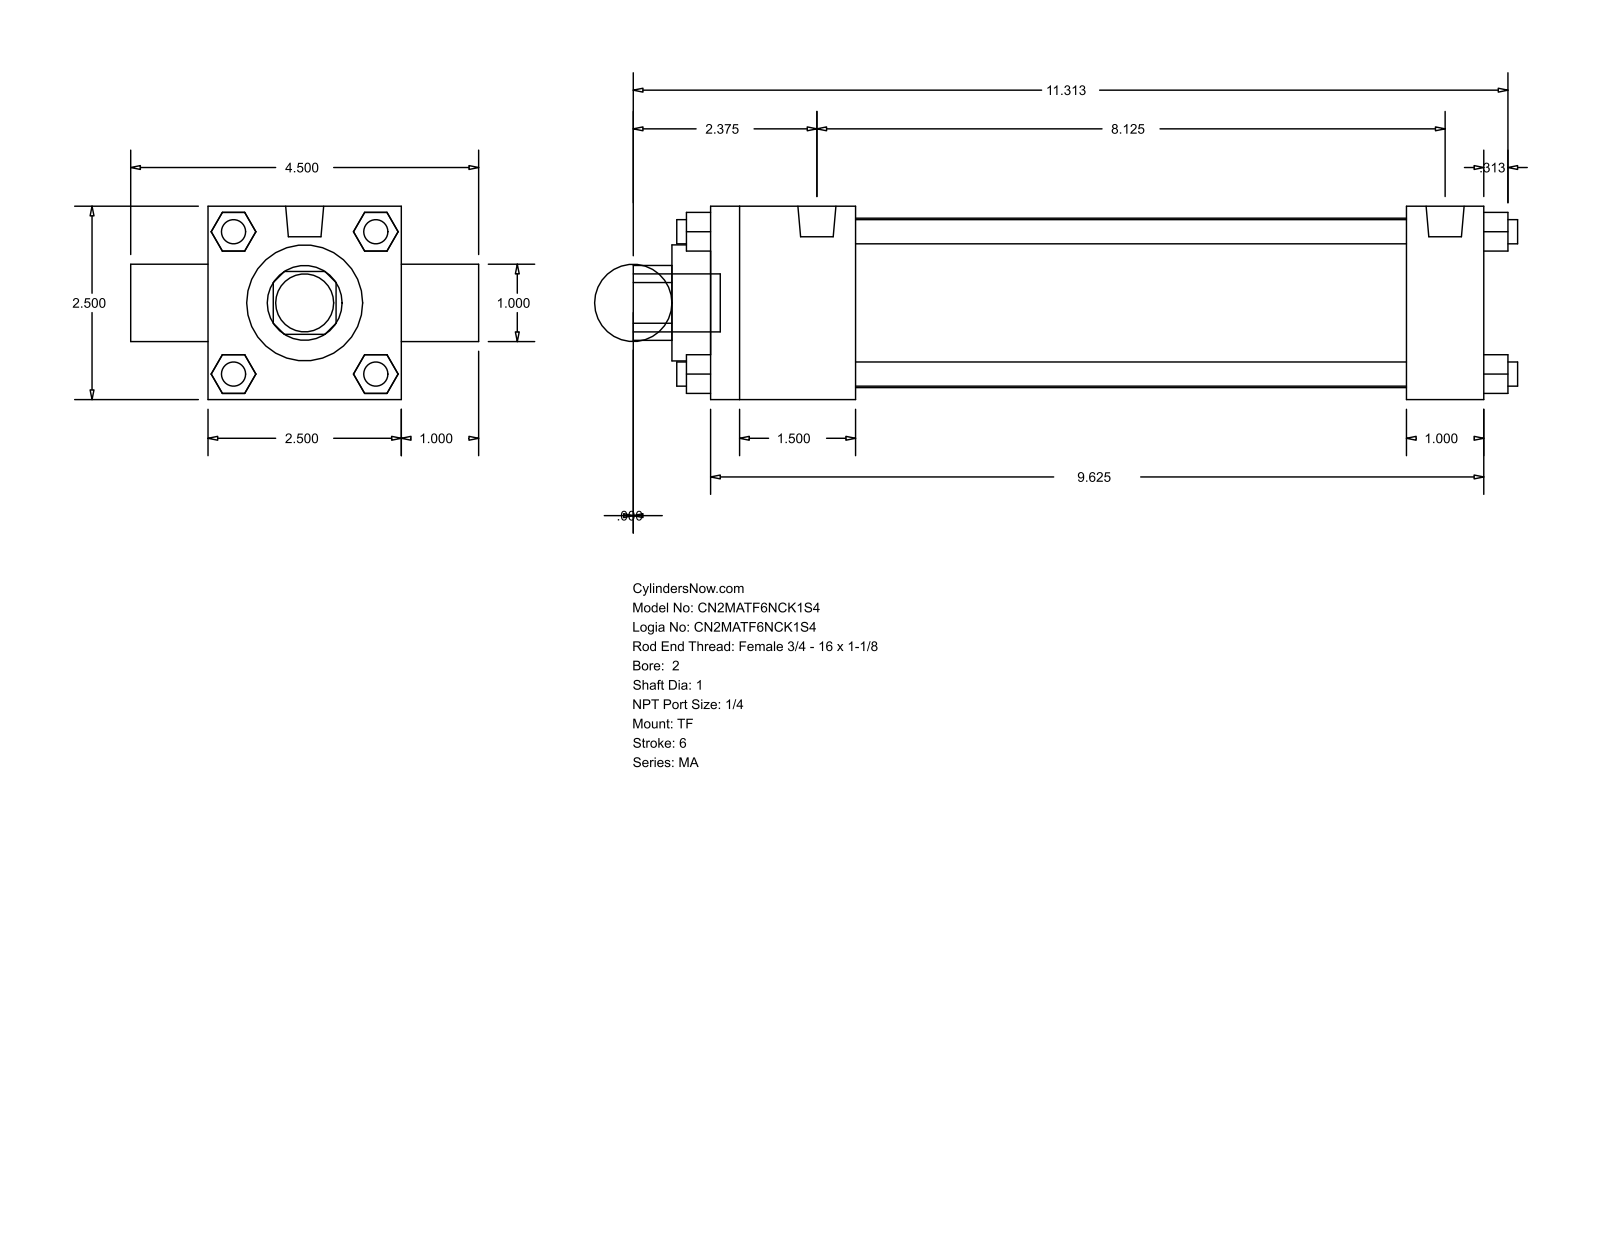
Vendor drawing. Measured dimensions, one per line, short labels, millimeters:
name: MA_TF__0200_1
written by: GSSL Pune (CONFIG_CONTROL_DESIGN)
unit: mm
bodies: 0 solids, 120 faces (92 planar, 28 cylindrical, 0 other)
size: 290.51 × 114.3 × 63.5
holes: 2× ⌀25.4, 1× ⌀38.1, 1× ⌀55.63
bosses: 7× ⌀7.94, 2× ⌀12.49, 1× ⌀19.05
rounds: 1× R12.29
face distances: 63.5, 25.4, 254, 12.7, 47.63, 228.6, 180.97, 206.37, 88.9, 23.37
